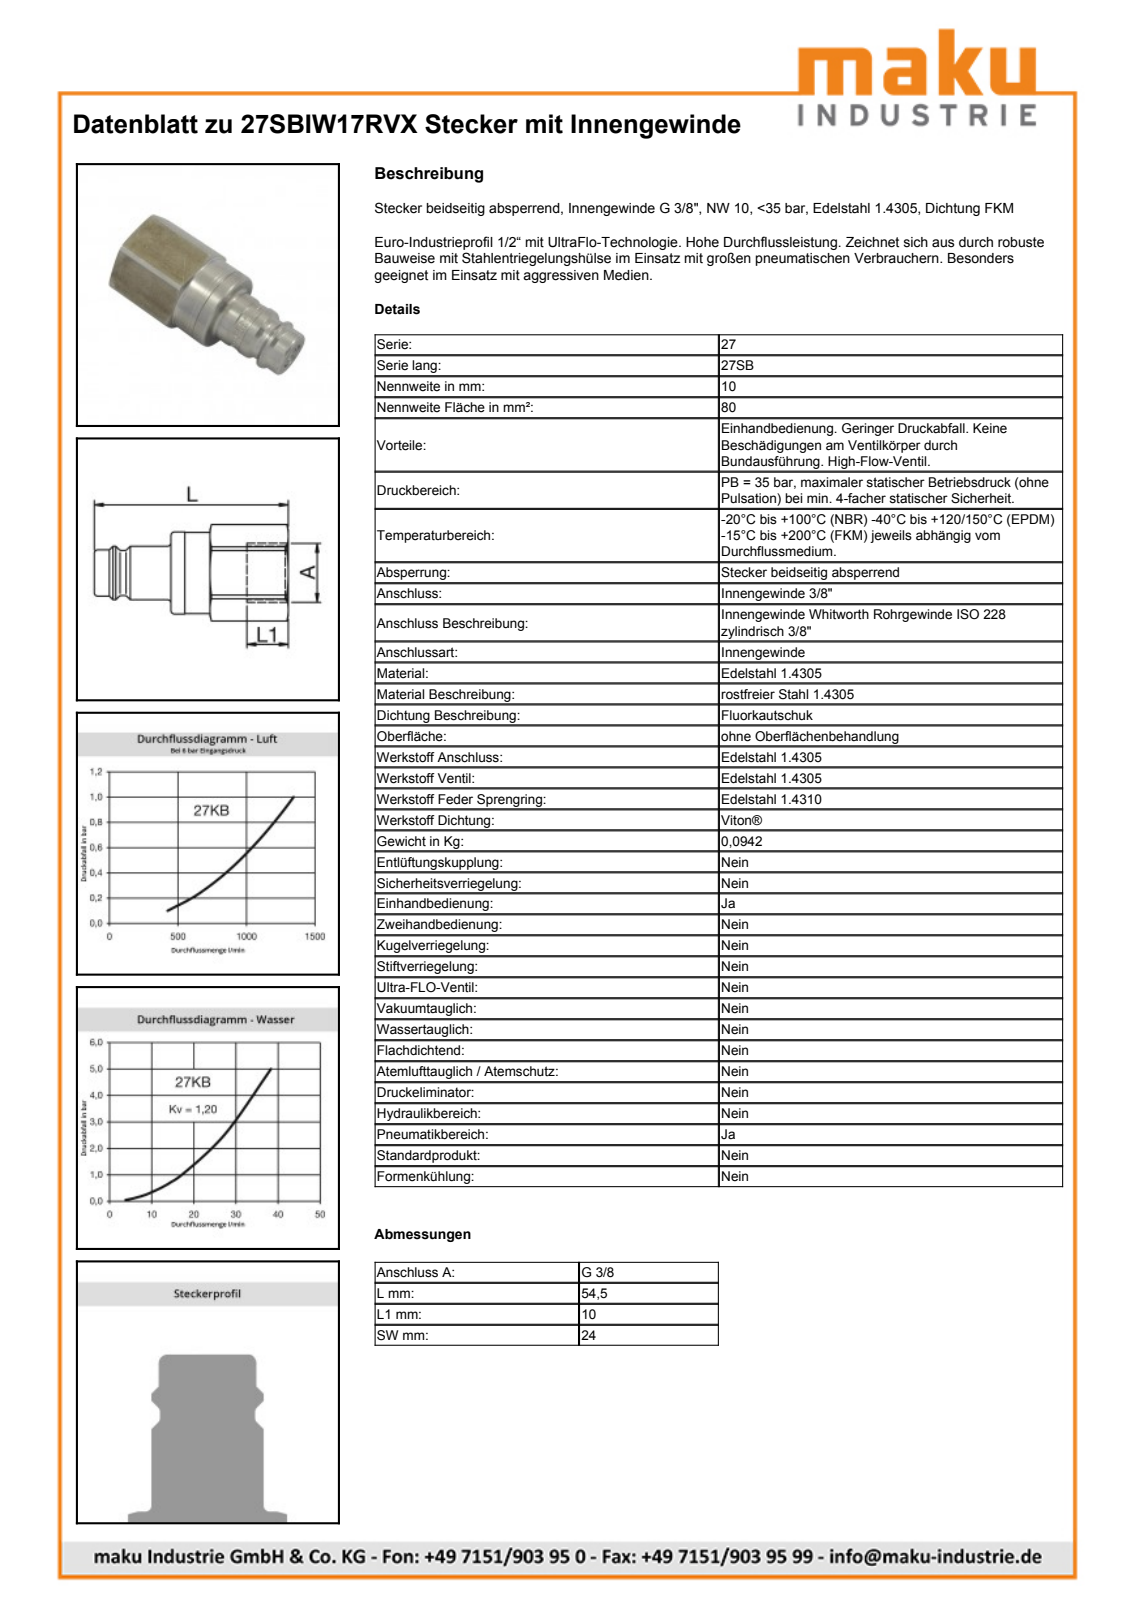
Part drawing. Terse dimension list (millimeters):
name: D106289
written by: Autodesk Inventor 2011 (AUTOMOTIVE_DESIGN)
unit: mm
bodies: 1 solid, 236 faces (98 planar, 39 cylindrical, 99 other)
size: 55.4 × 26.83 × 25.77
volume: 17 208 mm³; area: 5 218 mm²
holes: 1× ⌀14.95, 1× ⌀20.3
bosses: 1× ⌀23, 1× ⌀22.75, 1× ⌀19.88, 1× ⌀15, 1× ⌀14.5, 1× ⌀13, 1× ⌀12.65
rounds: 1× R7.15, 1× R13.53
face distances: 24.02, 24, 23.98, 11.72, 22.18, 33.9, 21.5, 43.68, 55.4, 32.45
